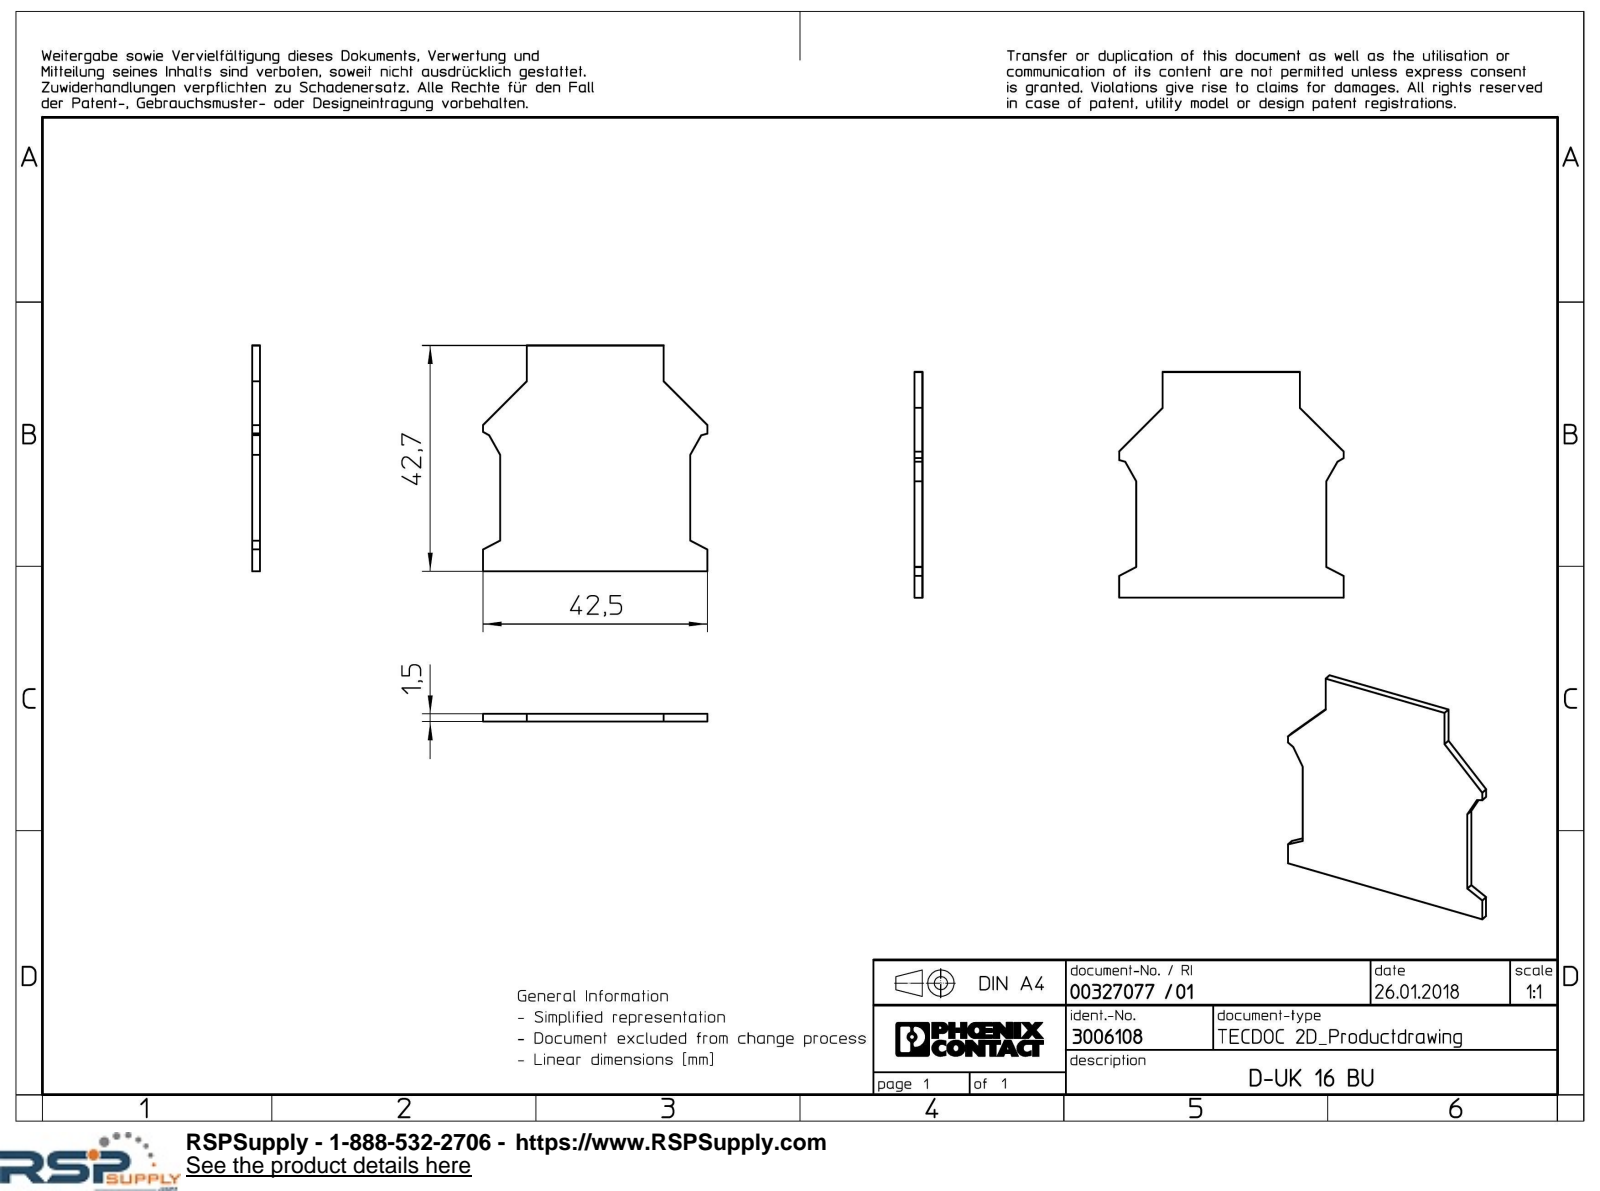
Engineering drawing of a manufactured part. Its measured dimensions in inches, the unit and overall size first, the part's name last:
Units: inches
Overall size (bounding box): 1.681 × 1.673 × 0.059
Main face-to-face distances: 0.059, 1.681, 1.417, 0.197, 1.22, 0.128, 0.325, 1.348, 1.545, 1.024
Volume: 0.138 in³ · Surface area: 5.061 in²
Bodies: 1 solid, 20 faces (20 planar, 0 cylindrical, 0 other)
Part name (STEP PRODUCT): D_UK_16_BU-select
STEP written by: Creo Elements/Direct Modeling 18.1I 14-Aug-2016 (C) Parametric Technology GmbH (AUTOMOTIVE_DESIGN)
